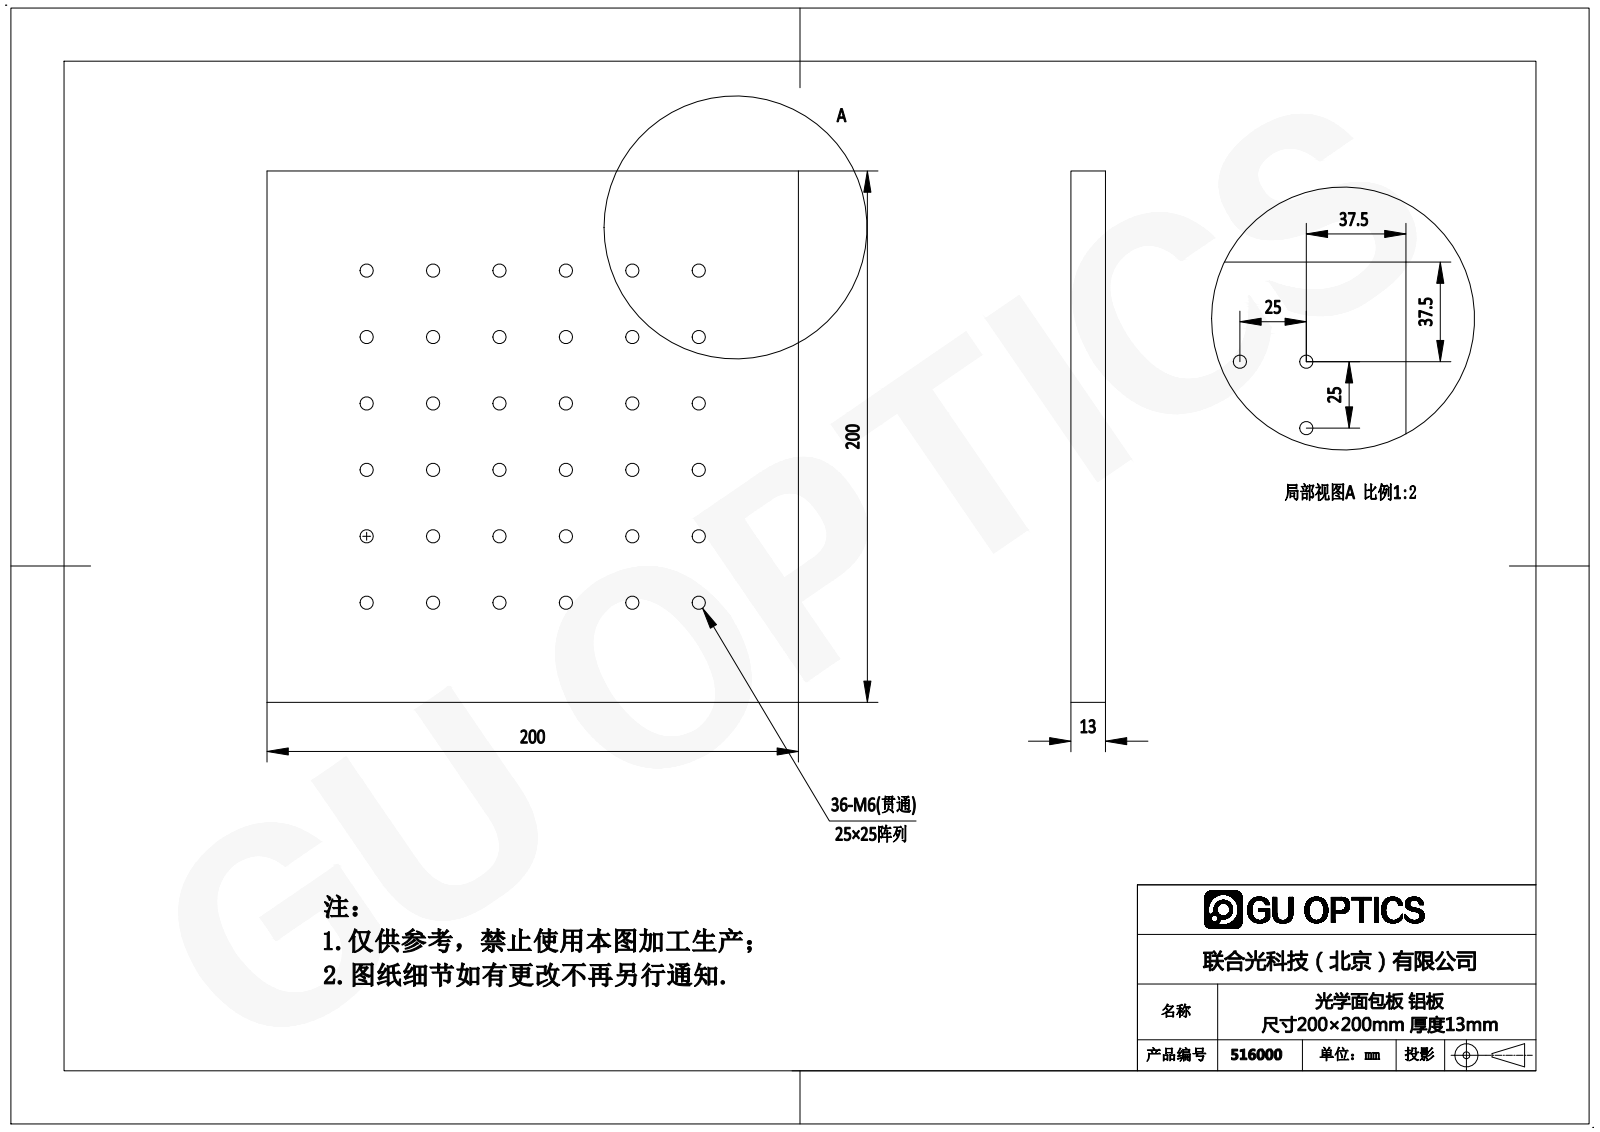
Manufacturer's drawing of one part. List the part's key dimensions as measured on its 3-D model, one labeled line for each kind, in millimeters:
Part name (STEP PRODUCT): 516000
STEP written by: SolidWorks 2016 (AUTOMOTIVE_DESIGN)
Units: millimetres
Bodies: 1 solid, 78 faces (6 planar, 72 cylindrical, 0 other)
Overall size (bounding box): 200 × 200 × 13
Volume: 510 811 mm³ · Surface area: 96 338 mm²
Round holes (diameter × count): ⌀5 ×36
Main face-to-face distances: 13, 200
Hole centre spacings: 55.9, 25, 79.06, 35.36, 50, 90.14, 75, 103.08
